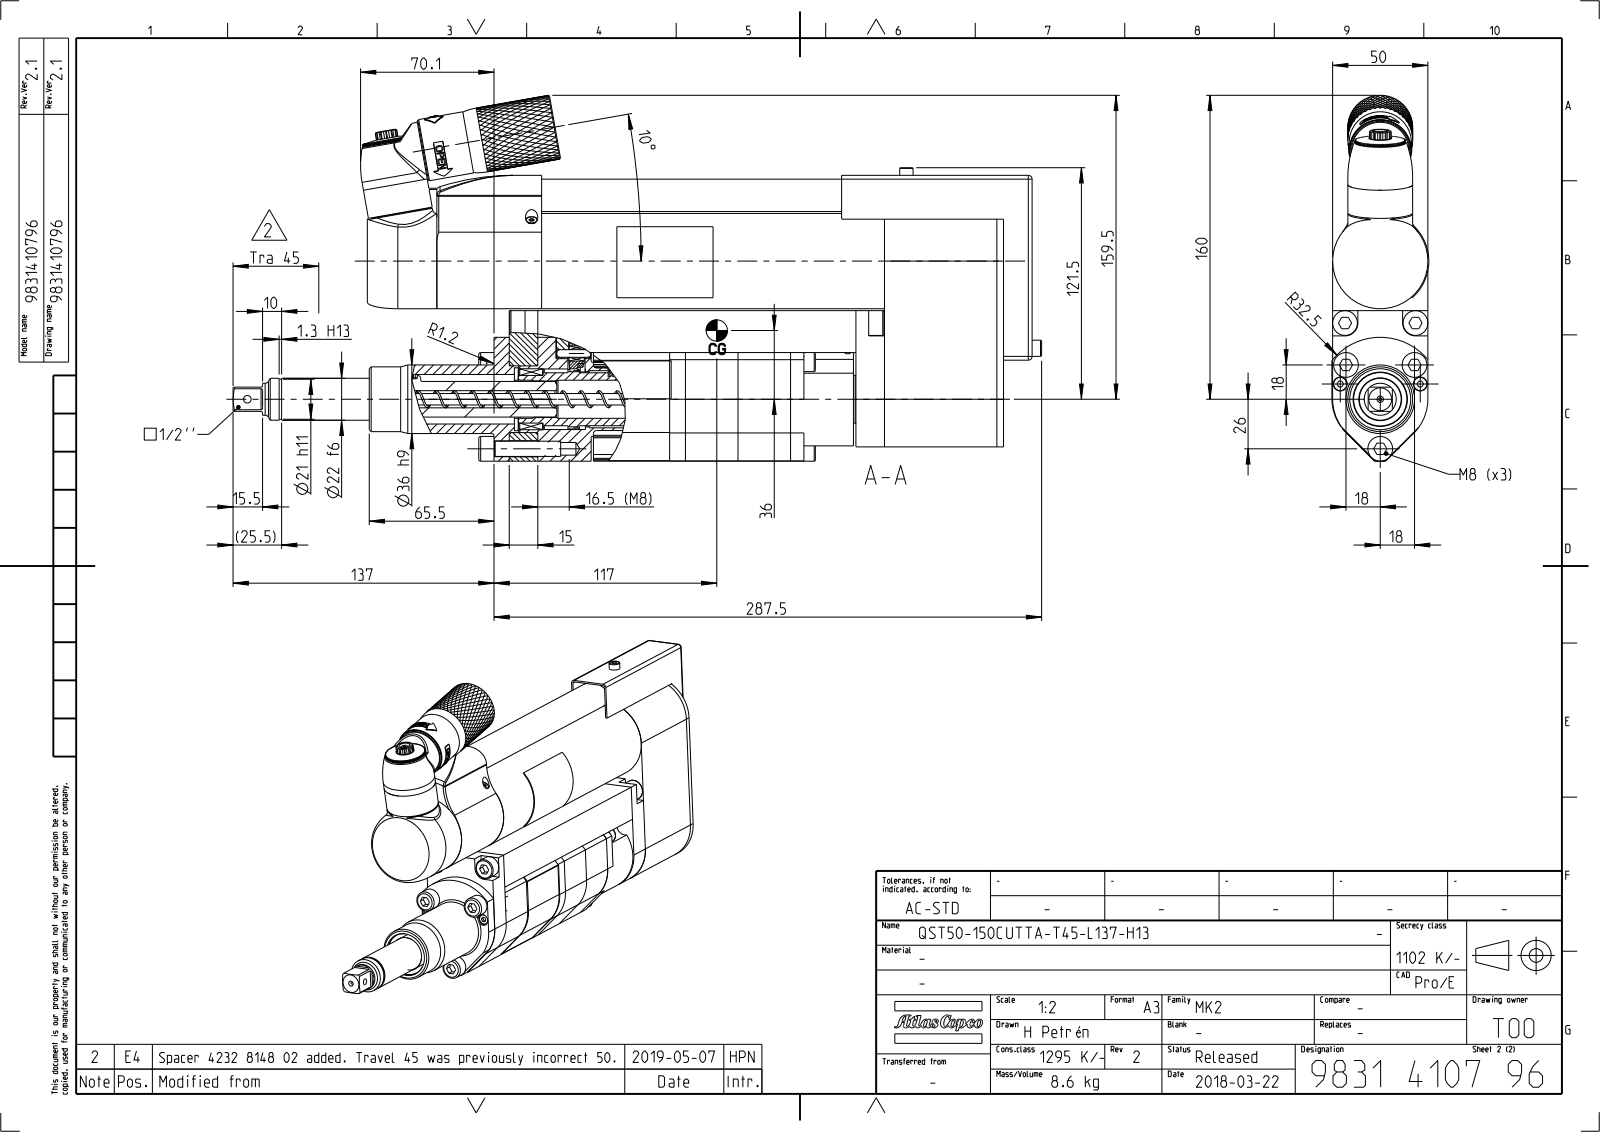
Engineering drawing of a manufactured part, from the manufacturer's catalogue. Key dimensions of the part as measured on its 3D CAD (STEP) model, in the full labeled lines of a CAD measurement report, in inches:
Part name (STEP PRODUCT): 4230260202; 4230260212_ASM; 4230265900; 0219110017 (+8 more)
STEP written by: CREO PARAMETRIC BY PTC INC, 2018100 (CONFIG_CONTROL_DESIGN)
Units: inches
Bodies: 43 solids, 3783 faces (1280 planar, 1328 cylindrical, 1175 other)
Overall size (bounding box): 16.713 × 7.559 × 1.984
Volume: 58.59 in³ · Surface area: 701.1 in²
Round holes (diameter × count): ⌀0.154 ×17, ⌀0.217 ×8, ⌀0.13 ×7, ⌀0.177 ×7, ⌀0.315 ×6, ⌀0.157 ×5, ⌀0.335 ×5, ⌀0.354 ×5, ⌀0.128 ×4, ⌀0.194 ×4, ⌀0.055 ×3, ⌀0.115 ×3
Round bosses / shafts (diameter × count): ⌀0.197 ×18, ⌀0.118 ×6, ⌀0.512 ×5, ⌀0.157 ×5, ⌀1.339 ×4, ⌀0.315 ×4, ⌀0.236 ×4, ⌀0.394 ×3
Partial cylindrical surfaces — rounded edges, fillets, slot ends (radius × count): R0.02 ×35, R0.039 ×16, R0.079 ×16, R0.011 ×12, R0.02 ×12, R0.031 ×6, R0.008 ×4, R0.075 ×4
Main face-to-face distances: 1.969, 0.039, 0.098, 0.591, 0.138, 0.472, 7.165, 0.512, 1.398, 0.984
Hole centre spacings: 0.768, 1.33, 1.086, 1.483, 0.397, 0.719, 1.535, 3.306
